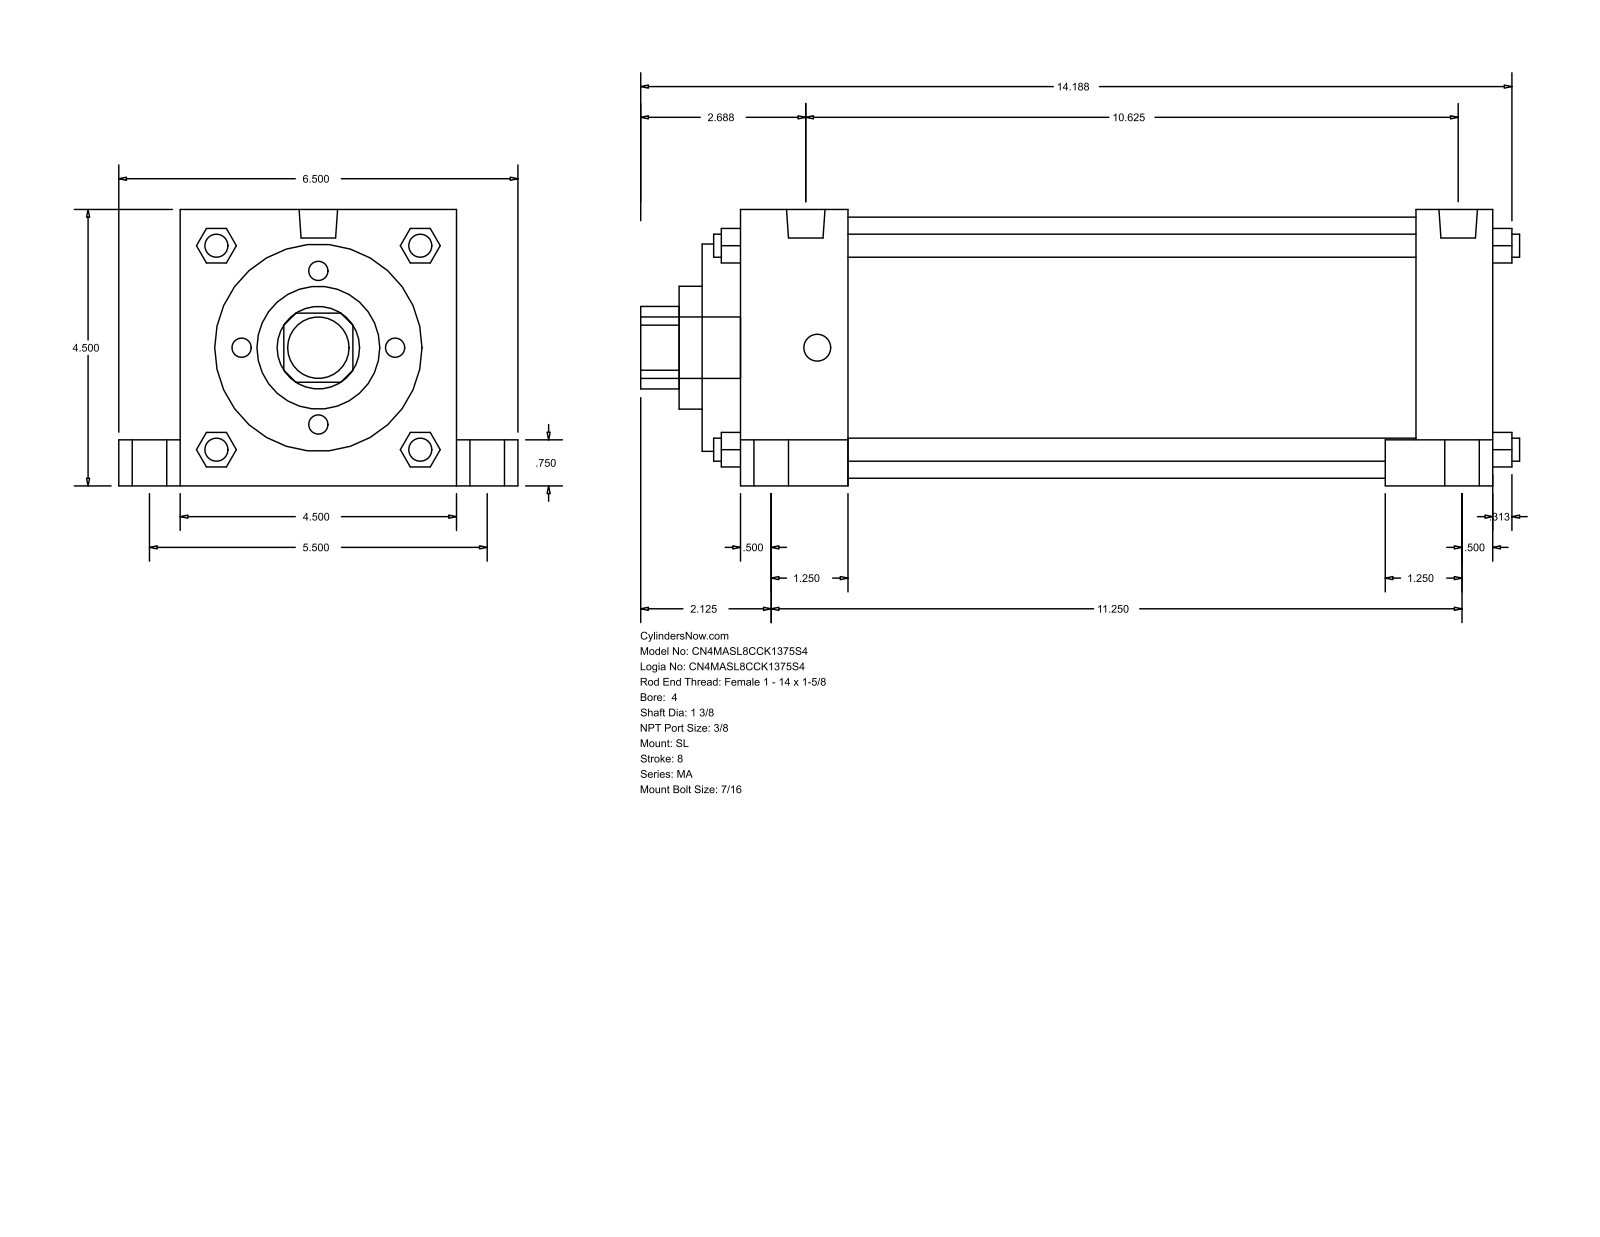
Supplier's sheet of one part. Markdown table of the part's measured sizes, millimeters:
| quantity | value |
| --- | --- |
| part name | MA_SL__0400_1.375 |
| STEP written by | GSSL Pune (CONFIG_CONTROL_DESIGN) |
| units | millimeters |
| bodies | 0 solids, 150 faces (113 planar, 37 cylindrical, 0 other) |
| overall size | 363.54 × 165.1 × 114.3 |
| round holes (diameter × count) | 34.92 × 1, 50.8 × 1, 85.72 × 1, 107.95 × 1 |
| round bosses / shafts (diameter × count) | 20.64 × 4, 14.29 × 4, 11.11 × 4, 9.53 × 4, 15.93 × 2, 25.4 × 1 |
| partial cylindrical surfaces (radius × count) | 17.06 × 1 |
| main face-to-face distances | 114.3, 311.16, 15.87, 327.03, 60.32, 44.45, 266.71, 295.28, 279.41, 234.96 |
